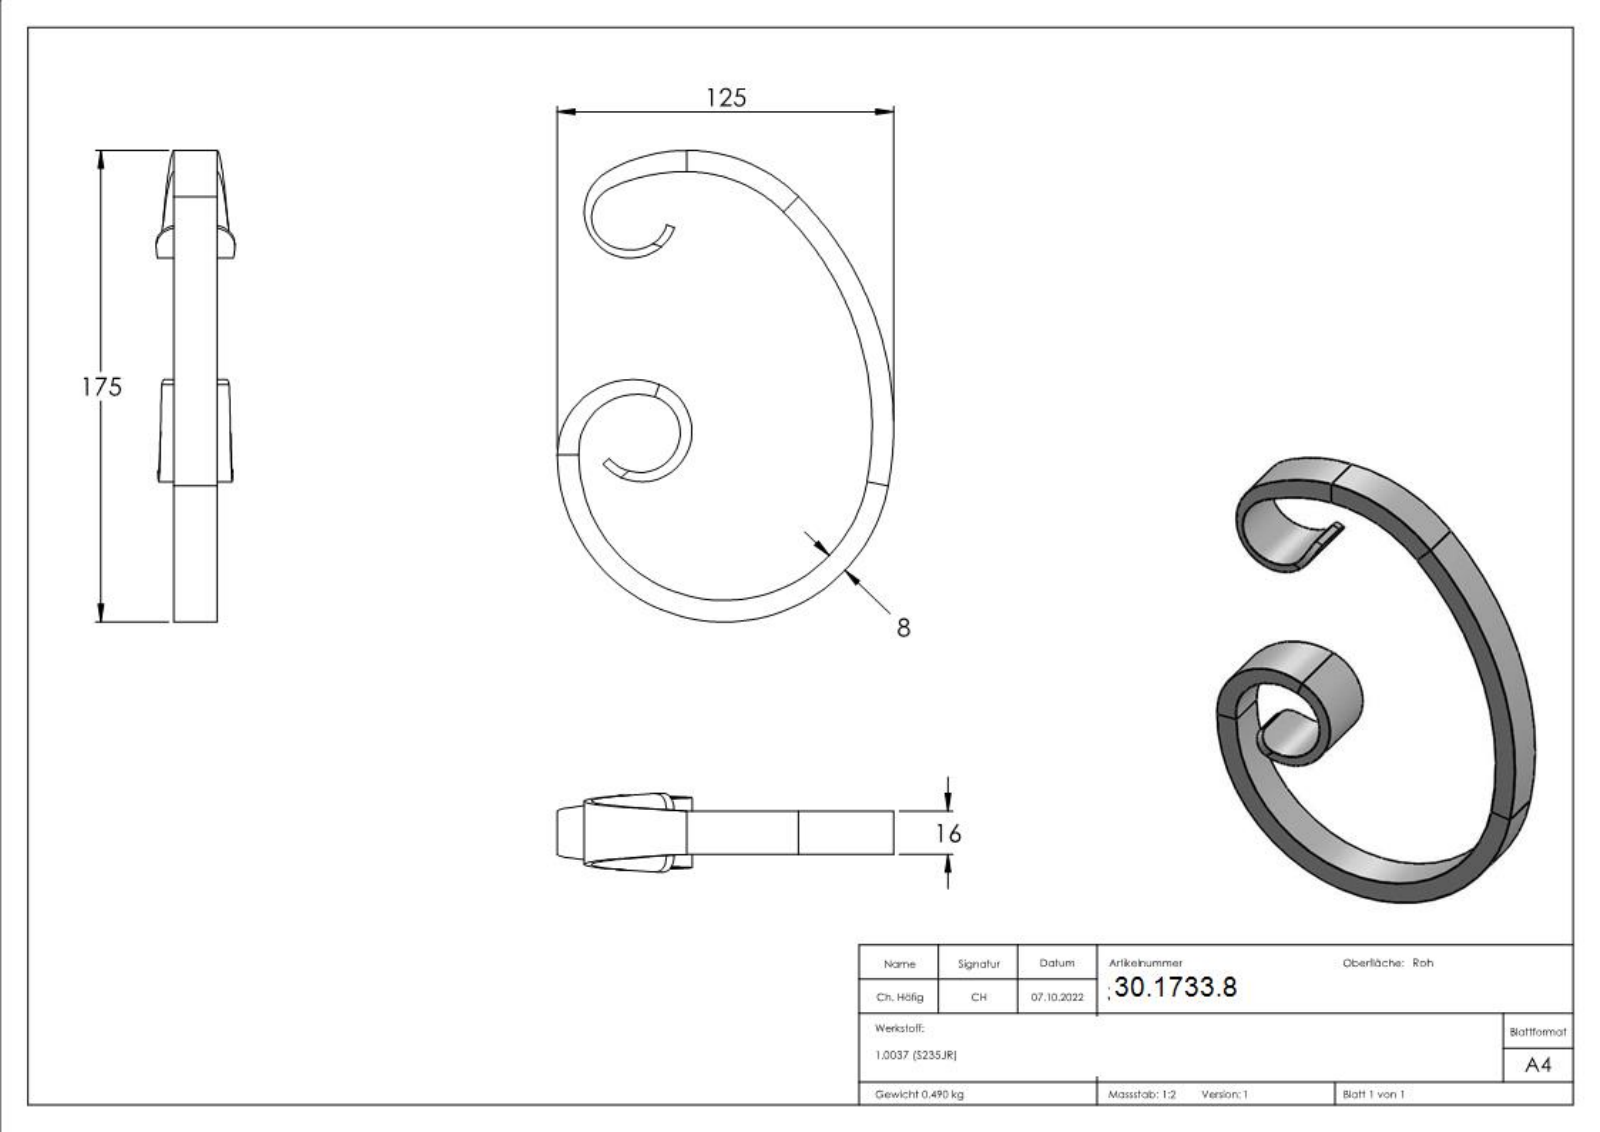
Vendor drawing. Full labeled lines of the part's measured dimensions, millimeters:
Part name (STEP PRODUCT): 3085
STEP written by: SolidWorks 2018 (CONFIG_CONTROL_DESIGN)
Units: millimetres
Bodies: 1 solid, 250 faces (93 planar, 25 cylindrical, 132 other)
Overall size (bounding box): 175 × 125 × 29.32
Volume: 62 881 mm³ · Surface area: 26 986 mm²
Partial cylindrical surfaces — rounded edges, fillets, slot ends (radius × count): R51 ×1, R54 ×1, R59 ×1, R62 ×1, R112 ×1, R112.1 ×1, R120 ×1
Main face-to-face distances: 16, 0.34, 6.99, 9.01, 0.32, 1.37, 0.58, 3.27, 2.2, 1.14
